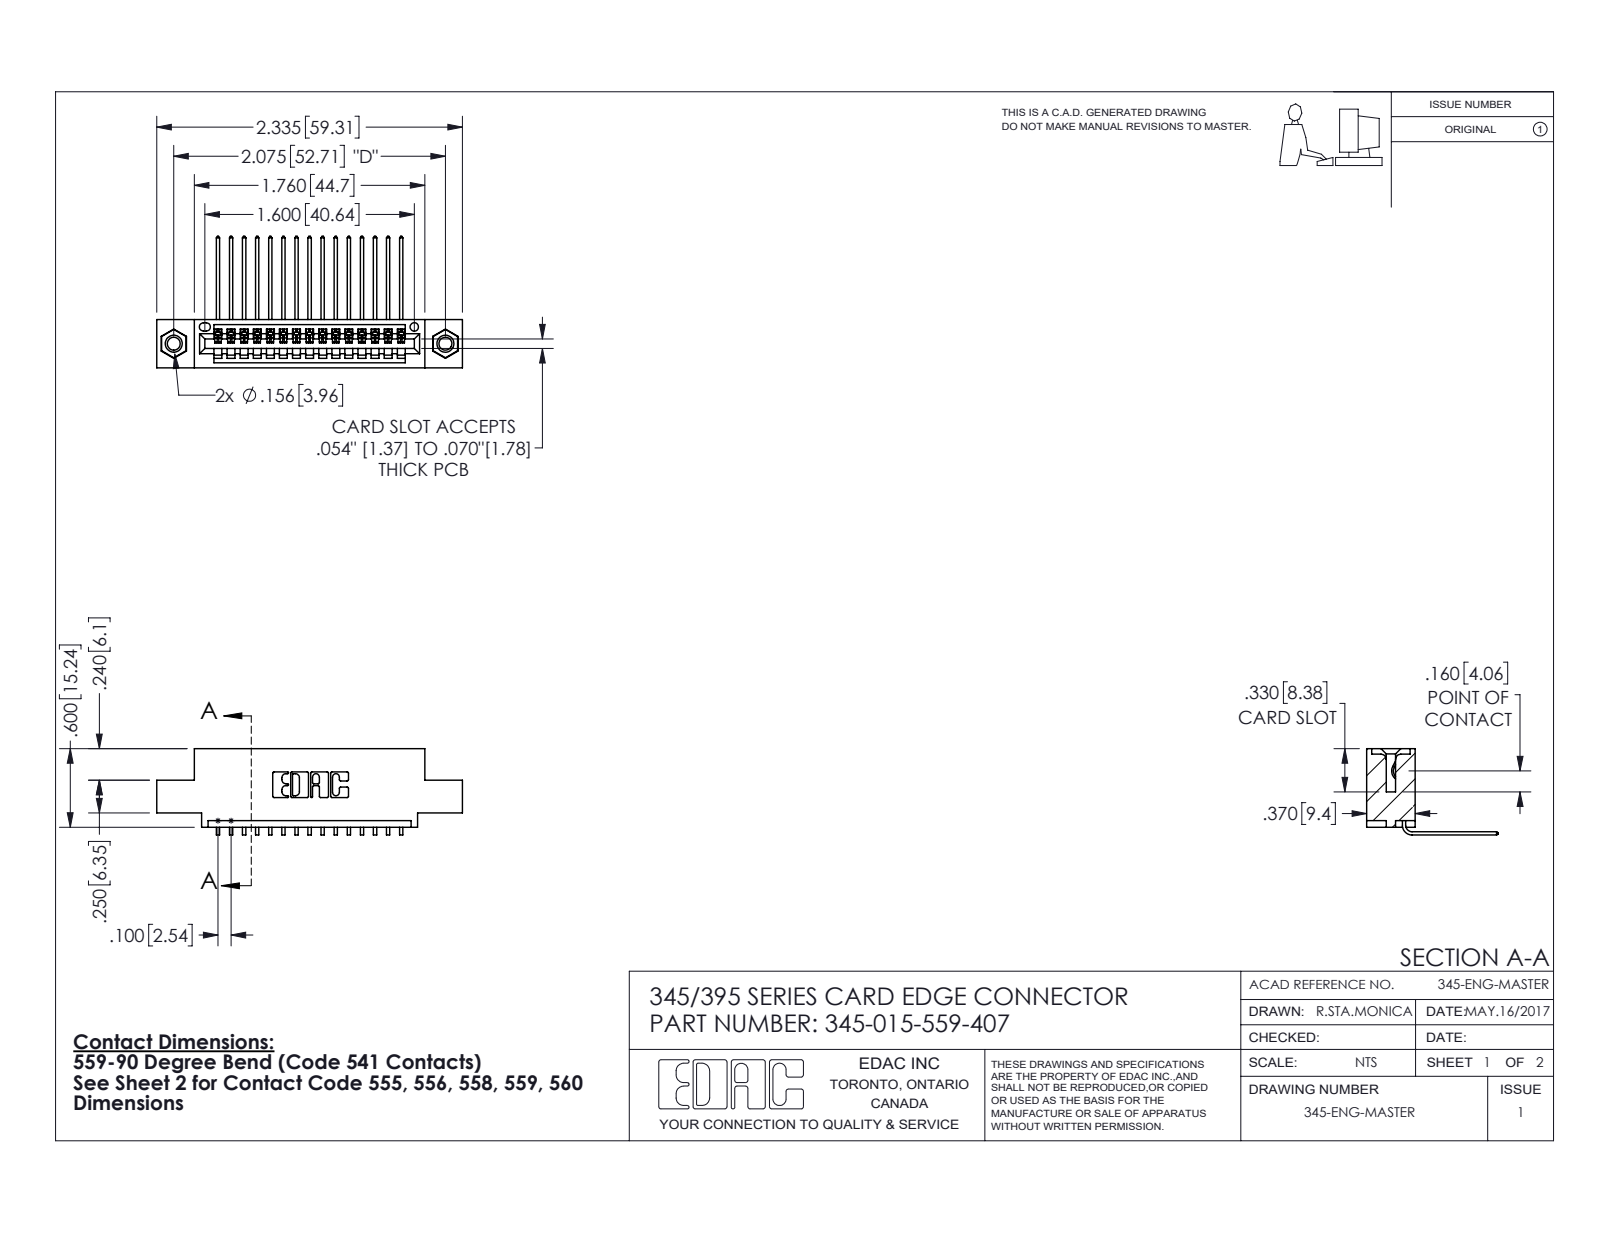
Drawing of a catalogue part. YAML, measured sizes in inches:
part_name: "345-292-001_558 559 Tail - 1; 345 Part_0.110 Offset - 0.156 Dia-TI; 345-250-001_345-250-005-103; 345-015-559-407"
step_written_by: "SolidWorks 2016 (CONFIG_CONTROL_DESIGN)"
units: inches
bodies: {solids: 18, faces: 1090, planar: 746, cylindrical: 328, other: 16}
overall_size: [2.335, 1.005, 0.659]
volume: 0.328
surface_area: 11.14
round_holes:
  - {diameter: 0.098, count: 2}
  - {diameter: 0.125, count: 2}
  - {diameter: 0.156, count: 2}
  - {diameter: 0.064, count: 1}
round_bosses_or_shafts:
  - {diameter: 0.155, count: 2}
partial_cylinders:
  - {radius: 0.006, count: 30}
  - {radius: 0.01, count: 22}
  - {radius: 0.007, count: 6}
  - {radius: 0.031, count: 6}
  - {radius: 0.026, count: 3}
  - {radius: 0.031, count: 2}
  - {radius: 0.04, count: 2}
  - {radius: 0.014, count: 1}
face_to_face_distances: [0.072, 0.298, 0.37, 0.2, 0.098, 0.272, 0.025, 0.1, 0.225, 0.16]
hole_center_spacings: [0.27, 1.842, 2.075]
